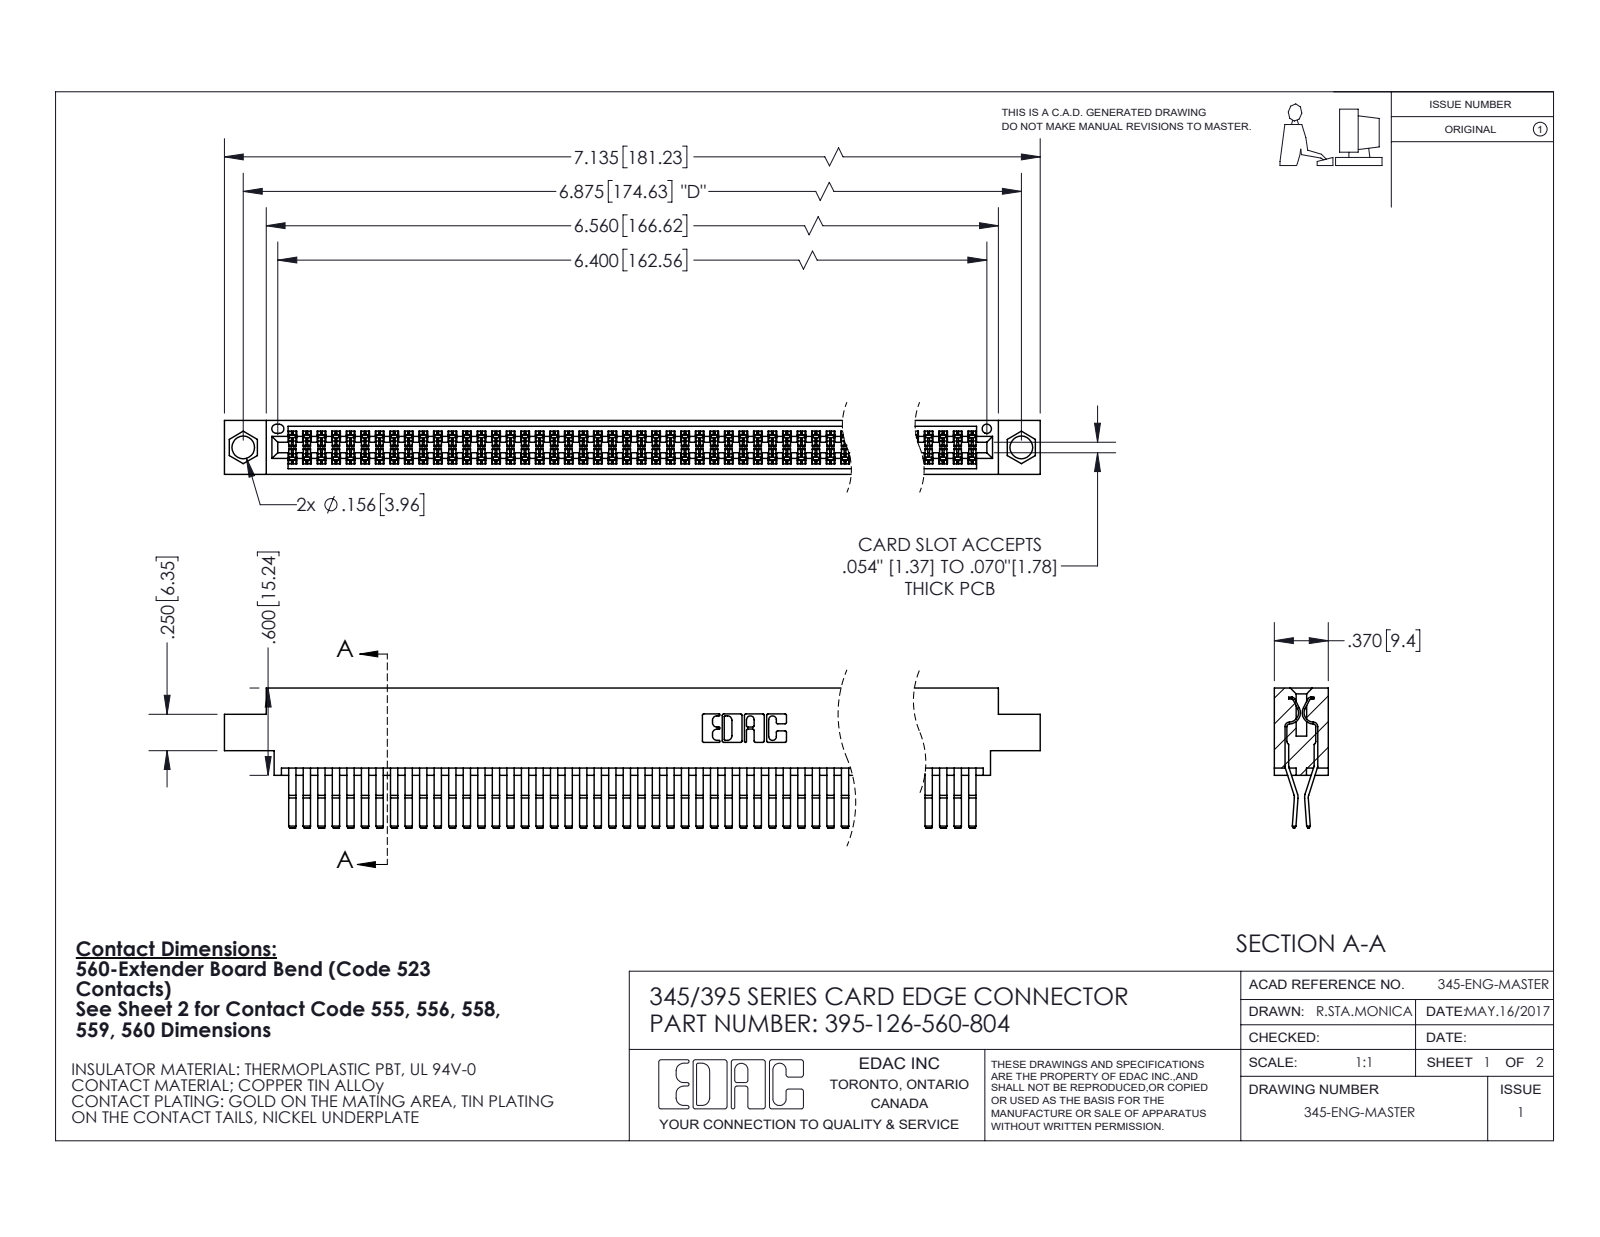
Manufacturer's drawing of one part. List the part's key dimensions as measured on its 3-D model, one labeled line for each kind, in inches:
Part name (STEP PRODUCT): 345 Part_0.170 Offset - 0.156 Dia-TI; 395-126-560-804; 345-292-001_560 Tail
STEP written by: SolidWorks 2020 (CONFIG_CONTROL_DESIGN)
Units: inches
Bodies: 127 solids, 6696 faces (4256 planar, 2440 cylindrical, 0 other)
Overall size (bounding box): 7.135 × 0.962 × 0.37
Volume: 1.123 in³ · Surface area: 46.09 in²
Round holes (diameter × count): ⌀0.156 ×2, ⌀0.064 ×1
Partial cylindrical surfaces — rounded edges, fillets, slot ends (radius × count): R0.006 ×252, R0.01 ×22, R0.007 ×6, R0.031 ×6, R0.026 ×3, R0.01 ×2, R0.014 ×2, R0.019 ×2
Main face-to-face distances: 0.025, 0.072, 0.298, 0.37, 0.2, 0.098, 0.272, 0.225, 0.175, 0.149
Hole centre spacings: 0.27, 6.639, 6.875
